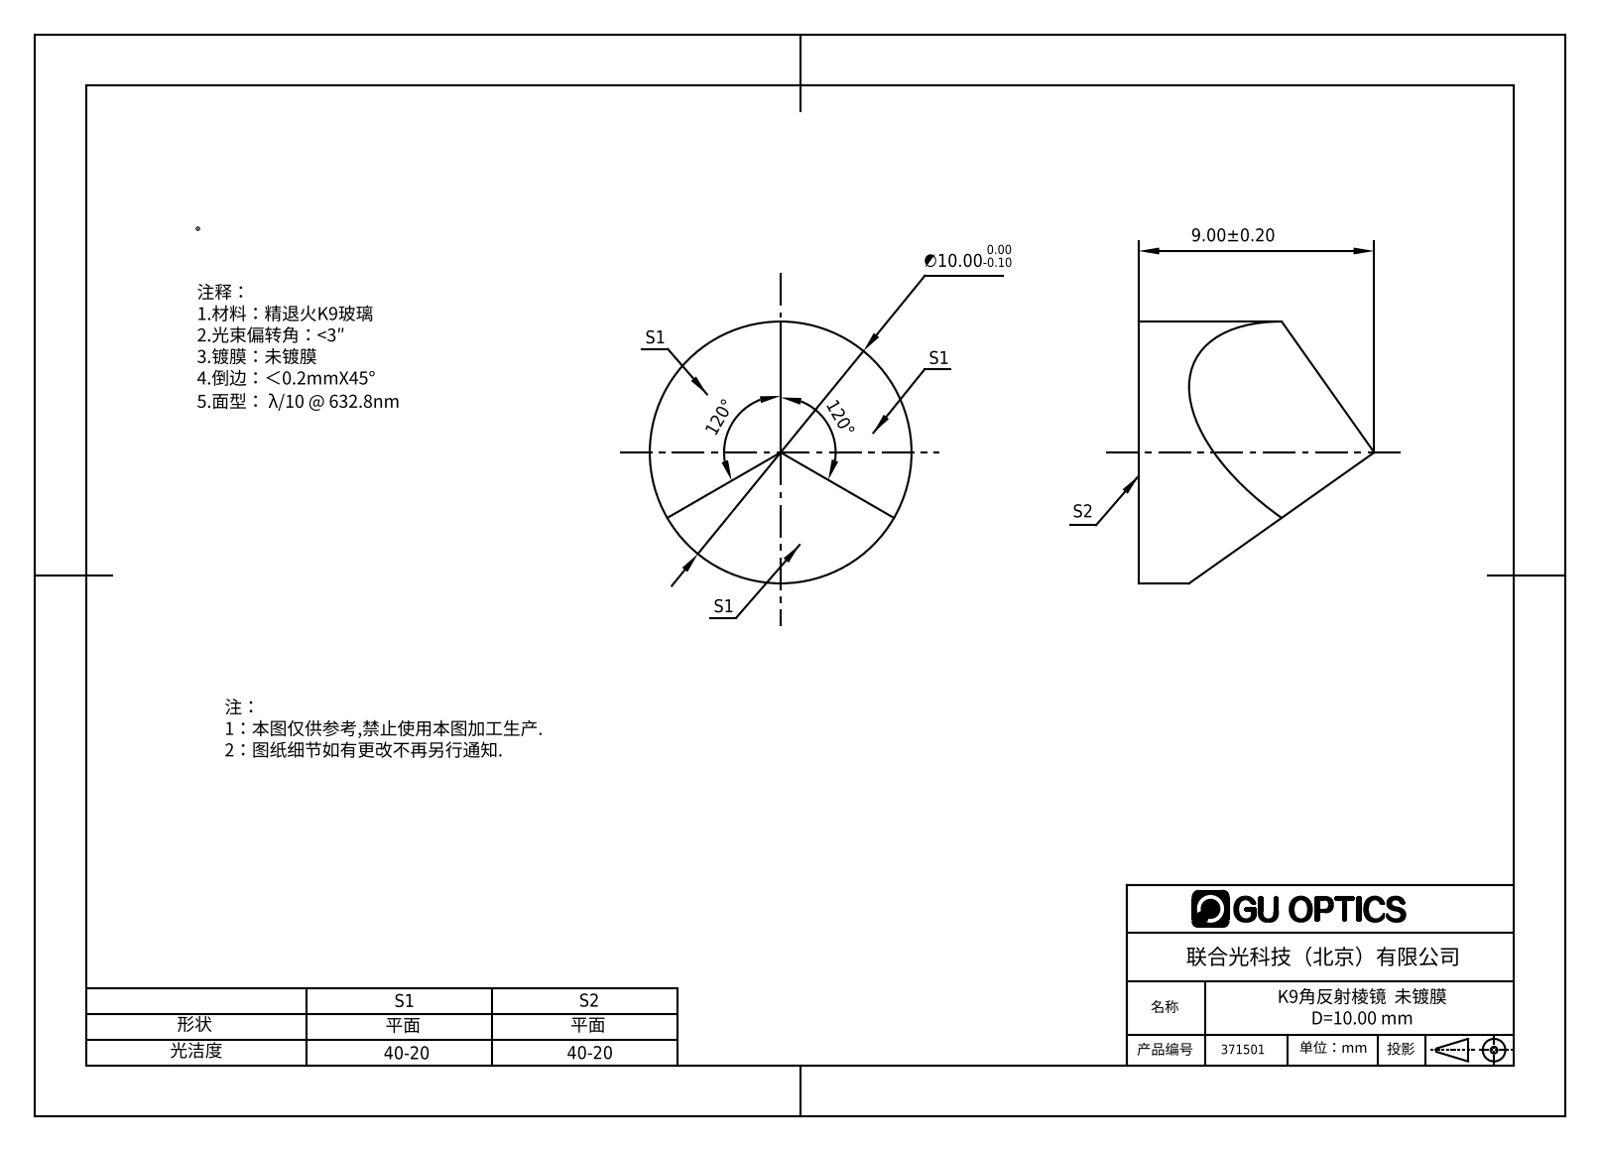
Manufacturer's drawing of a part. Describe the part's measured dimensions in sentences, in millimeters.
The part is named "371501". Its 3-D file was written by "SolidWorks 2016 (CONFIG_CONTROL_DESIGN)". It is 1 solid with 6 faces: 4 planar, 2 cylindrical and 0 other. Overall it measures 10 by 10 by 9 millimeters. Its volume is 401 cubic millimeters and its surface area 314 square millimeters. Round bosses or shafts: 1 of diameter 10.
